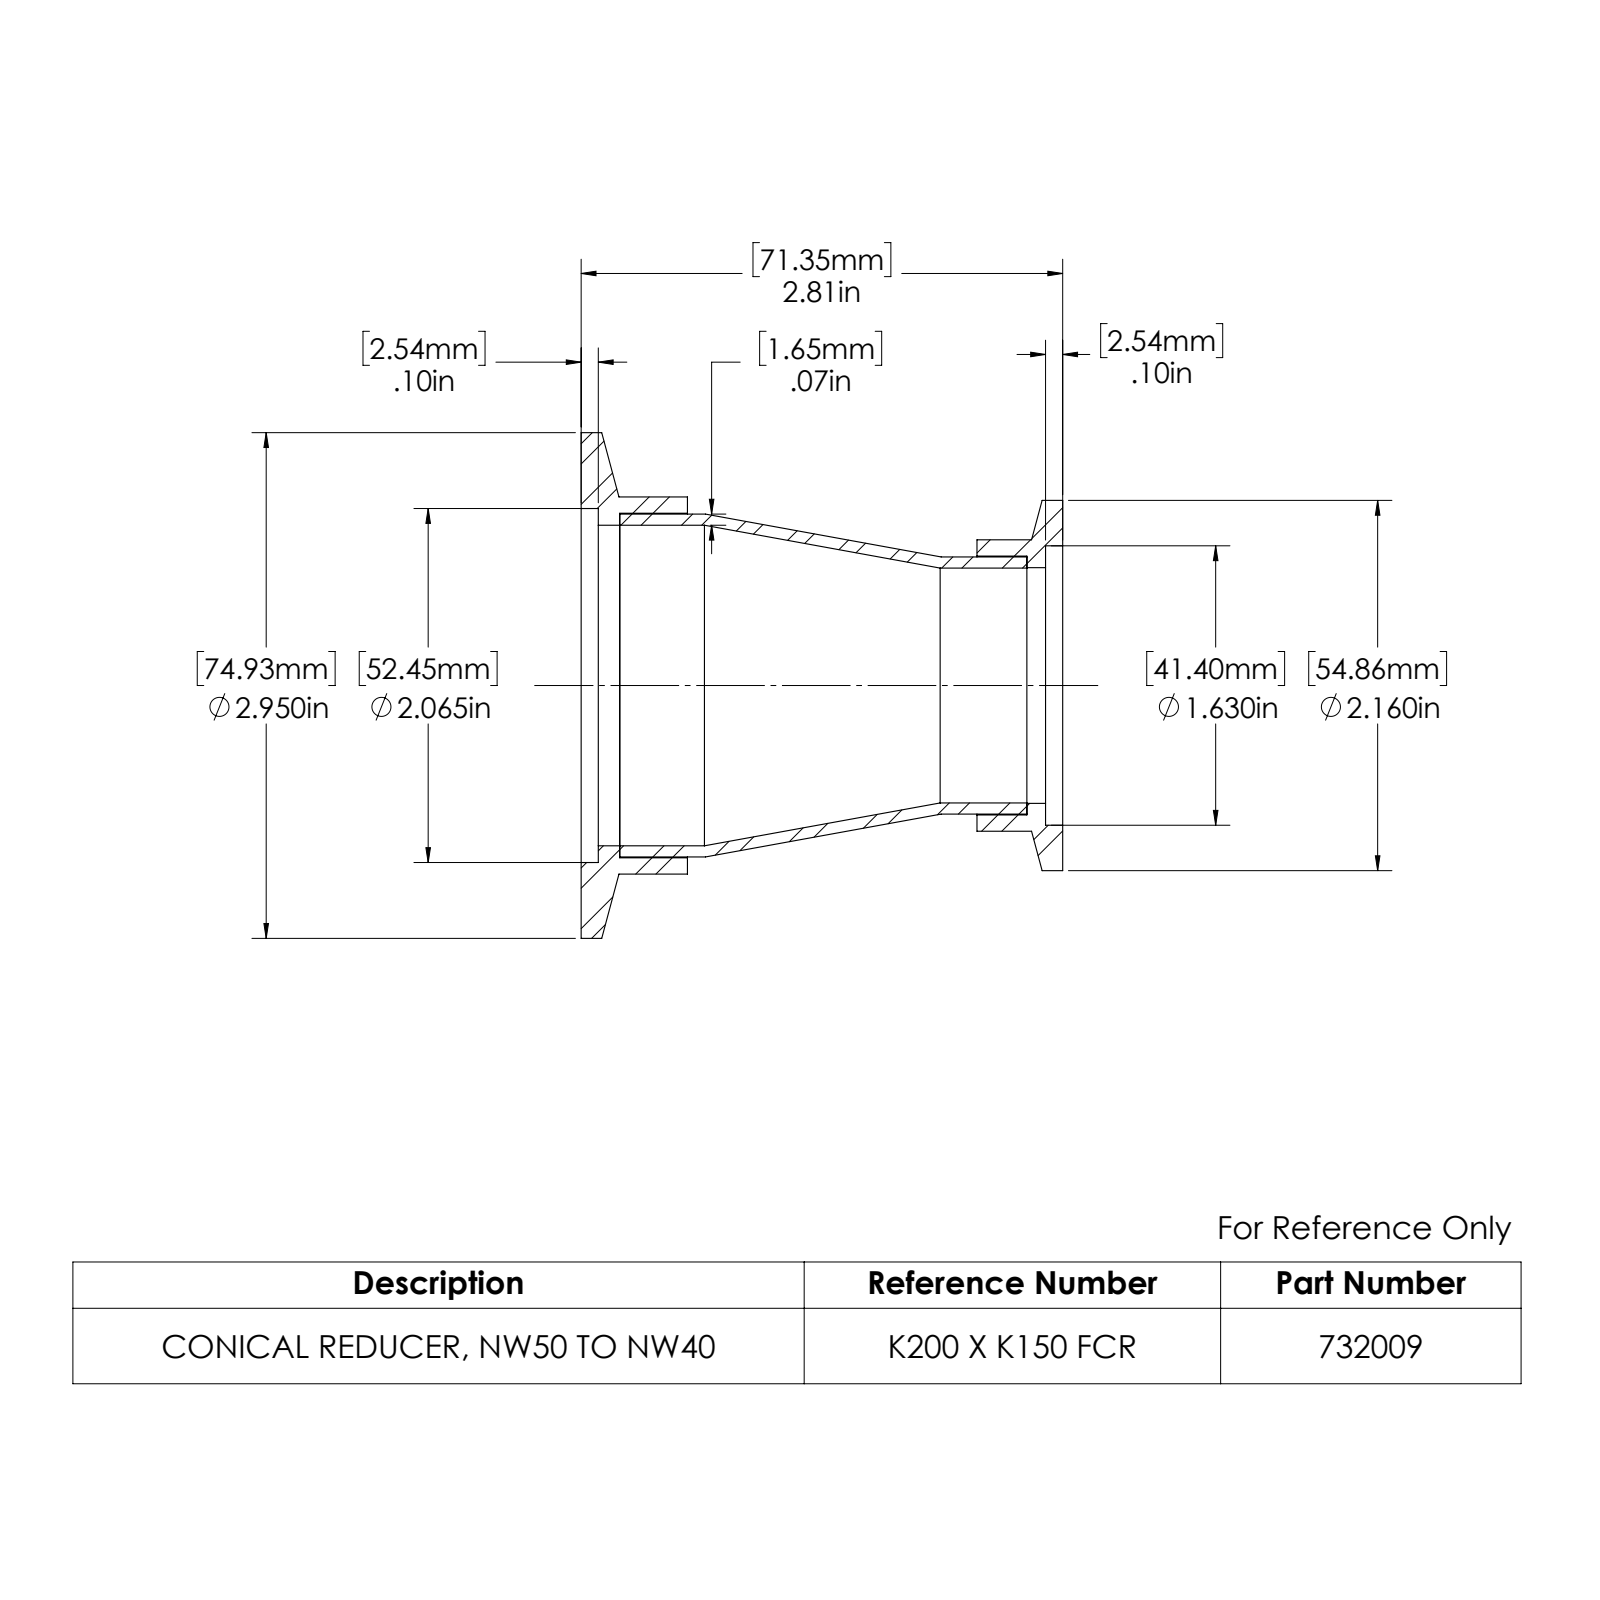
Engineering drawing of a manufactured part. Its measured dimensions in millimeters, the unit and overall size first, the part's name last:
Units: millimetres
Overall size (bounding box): 74.9 × 74.9 × 71.3
Round holes (diameter × count): ⌀34.8 ×1, ⌀34.9 ×1, ⌀38.4 ×1, ⌀41.4 ×1, ⌀47.5 ×1, ⌀51.1 ×1, ⌀52.5 ×1
Round bosses / shafts (diameter × count): ⌀74.9 ×1, ⌀55.9 ×1, ⌀54.9 ×1, ⌀50.8 ×1, ⌀43.2 ×1, ⌀38.1 ×1
Main face-to-face distances: 71.3, 2.5, 68.8, 5.7, 65.6, 15.7, 10, 55.6, 3.2, 13.2
Volume: 36 230 mm³ · Surface area: 33 150 mm²
Bodies: 3 solids, 46 faces (10 planar, 28 cylindrical, 8 other)
Part name (STEP PRODUCT): 713004; 402504; 713003; 732009
STEP written by: SolidWorks 2022 (AUTOMOTIVE_DESIGN)
